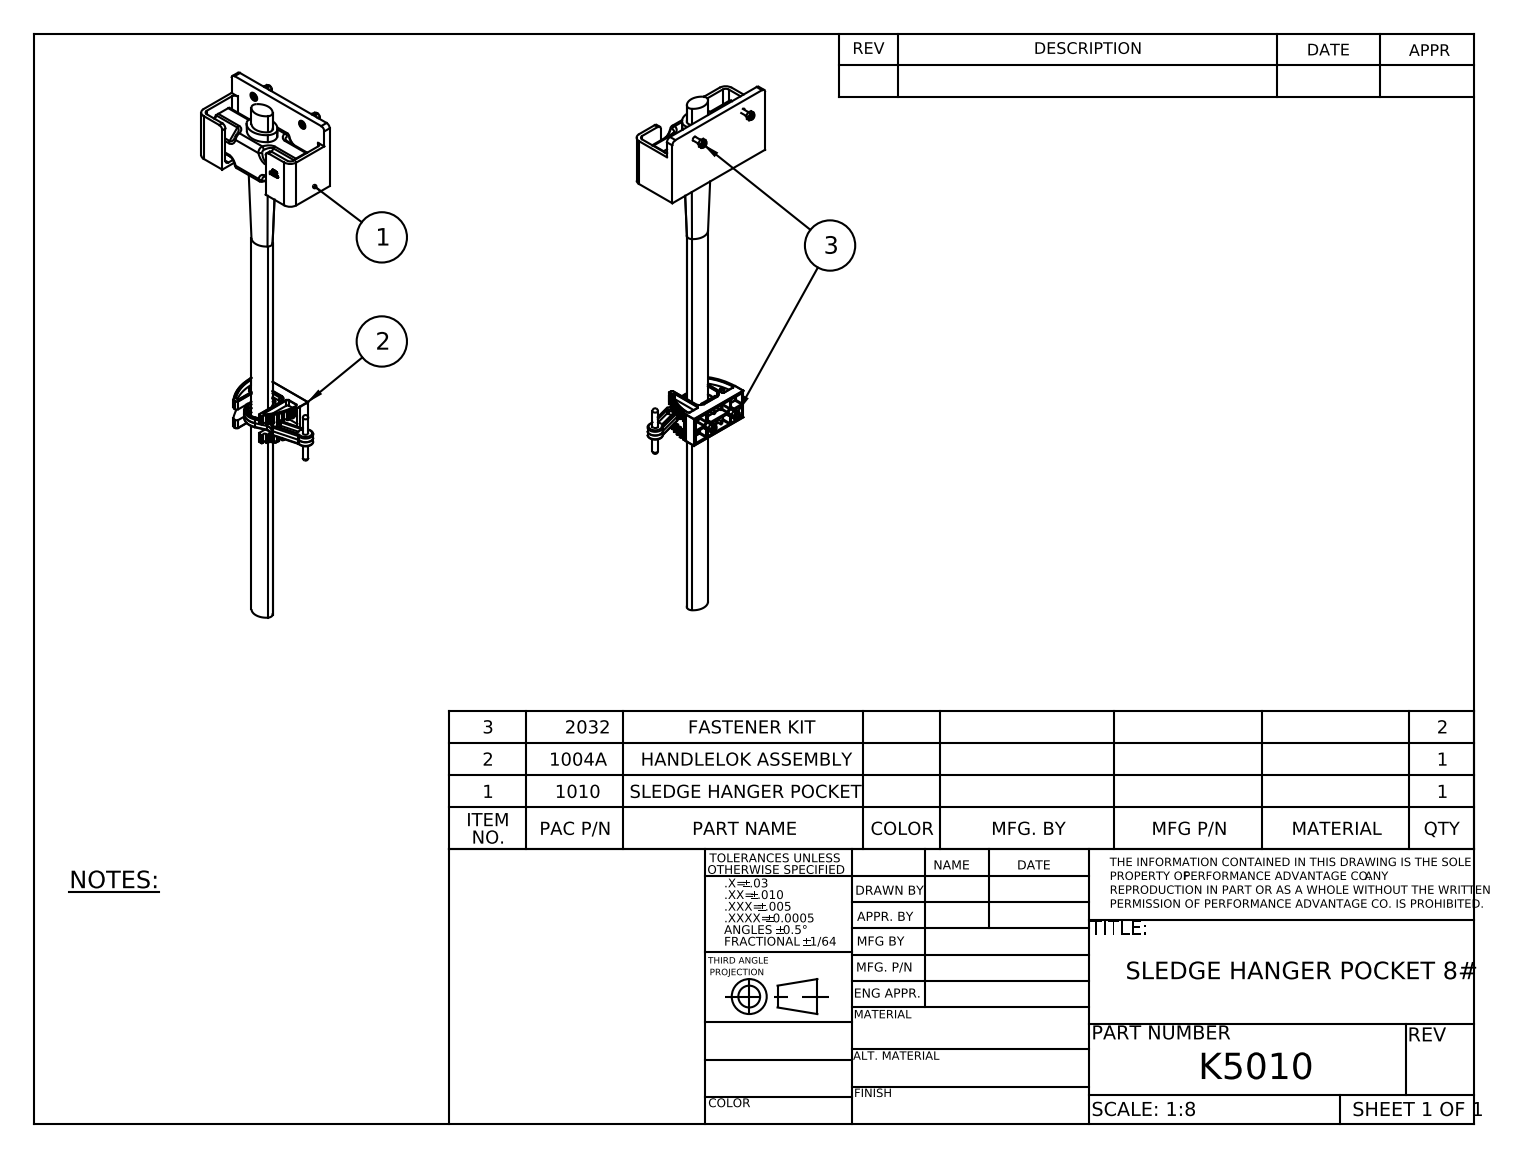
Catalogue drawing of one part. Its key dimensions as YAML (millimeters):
part_name: "K5010; 1010; sledge 2; 1004_In use (+8 more)"
step_written_by: "SolidWorks 2010 (CONFIG_CONTROL_DESIGN)"
units: millimeters
bodies: {solids: 17, faces: 1319, planar: 474, cylindrical: 456, other: 389}
overall_size: [892.2, 194.5, 101.7]
volume: 1686000
surface_area: 289100
round_holes:
  - {diameter: 6.4, count: 5}
  - {diameter: 4.3, count: 4}
  - {diameter: 5.1, count: 4}
  - {diameter: 6.8, count: 4}
  - {diameter: 6.8, count: 4}
  - {diameter: 4, count: 1}
  - {diameter: 4, count: 1}
  - {diameter: 8, count: 1}
round_bosses_or_shafts:
  - {diameter: 11.5, count: 4}
  - {diameter: 10.3, count: 4}
  - {diameter: 4.7, count: 4}
  - {diameter: 4.1, count: 4}
  - {diameter: 5.2, count: 3}
  - {diameter: 15.9, count: 1}
  - {diameter: 6.4, count: 1}
  - {diameter: 5.2, count: 1}
partial_cylinders:
  - {radius: 0.4, count: 68}
  - {radius: 1, count: 32}
  - {radius: 6.4, count: 15}
  - {radius: 3.2, count: 12}
  - {radius: 1.6, count: 10}
  - {radius: 1.6, count: 9}
  - {radius: 10.2, count: 8}
  - {radius: 1.7, count: 7}
face_to_face_distances: [6.4, 11.1, 63.5, 69.9, 74.6, 68.1, 61.7, 3.2, 44.5, 184.2]
hole_center_spacings: [21, 33.5, 14.3, 25.4, 29.1, 511.4, 512.8, 523]
